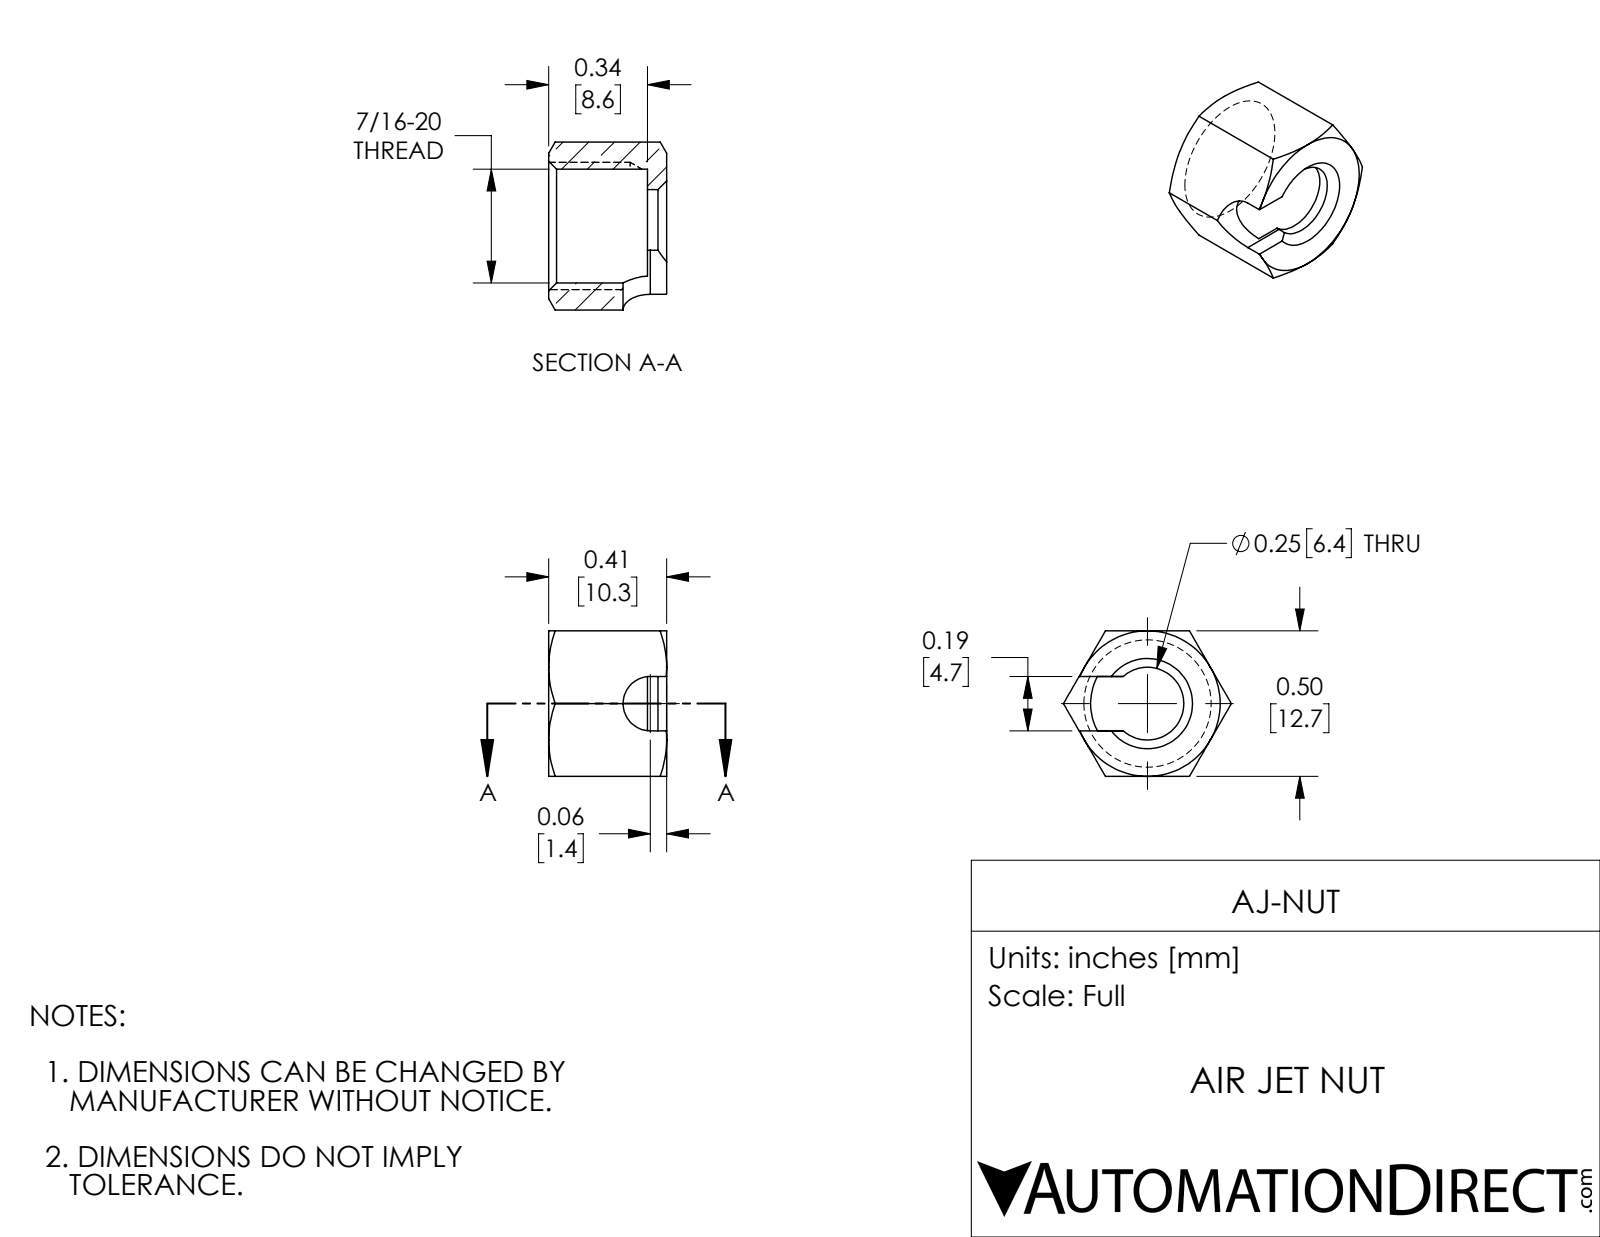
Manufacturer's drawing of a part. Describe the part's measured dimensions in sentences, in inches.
The part is named "AJ-NUT". Its 3-D file was written by "SolidWorks 2018 (AUTOMOTIVE_DESIGN)". It is 1 solid with 34 faces: 11 planar, 5 cylindrical and 18 other. Overall it measures 0.577 by 0.5 by 0.406 inches. Its volume is 0.04 cubic inches and its surface area 1.403 square inches. Round holes: 1 of diameter 0.391. Partial cylindrical surfaces (rounded edges, fillets, slot ends): 1 of radius 0.094, 1 of radius 0.125. The main face-to-face distances are 0.5, 0.066, 0.34, 0.406, 0.157, 0.343, 0.187.
